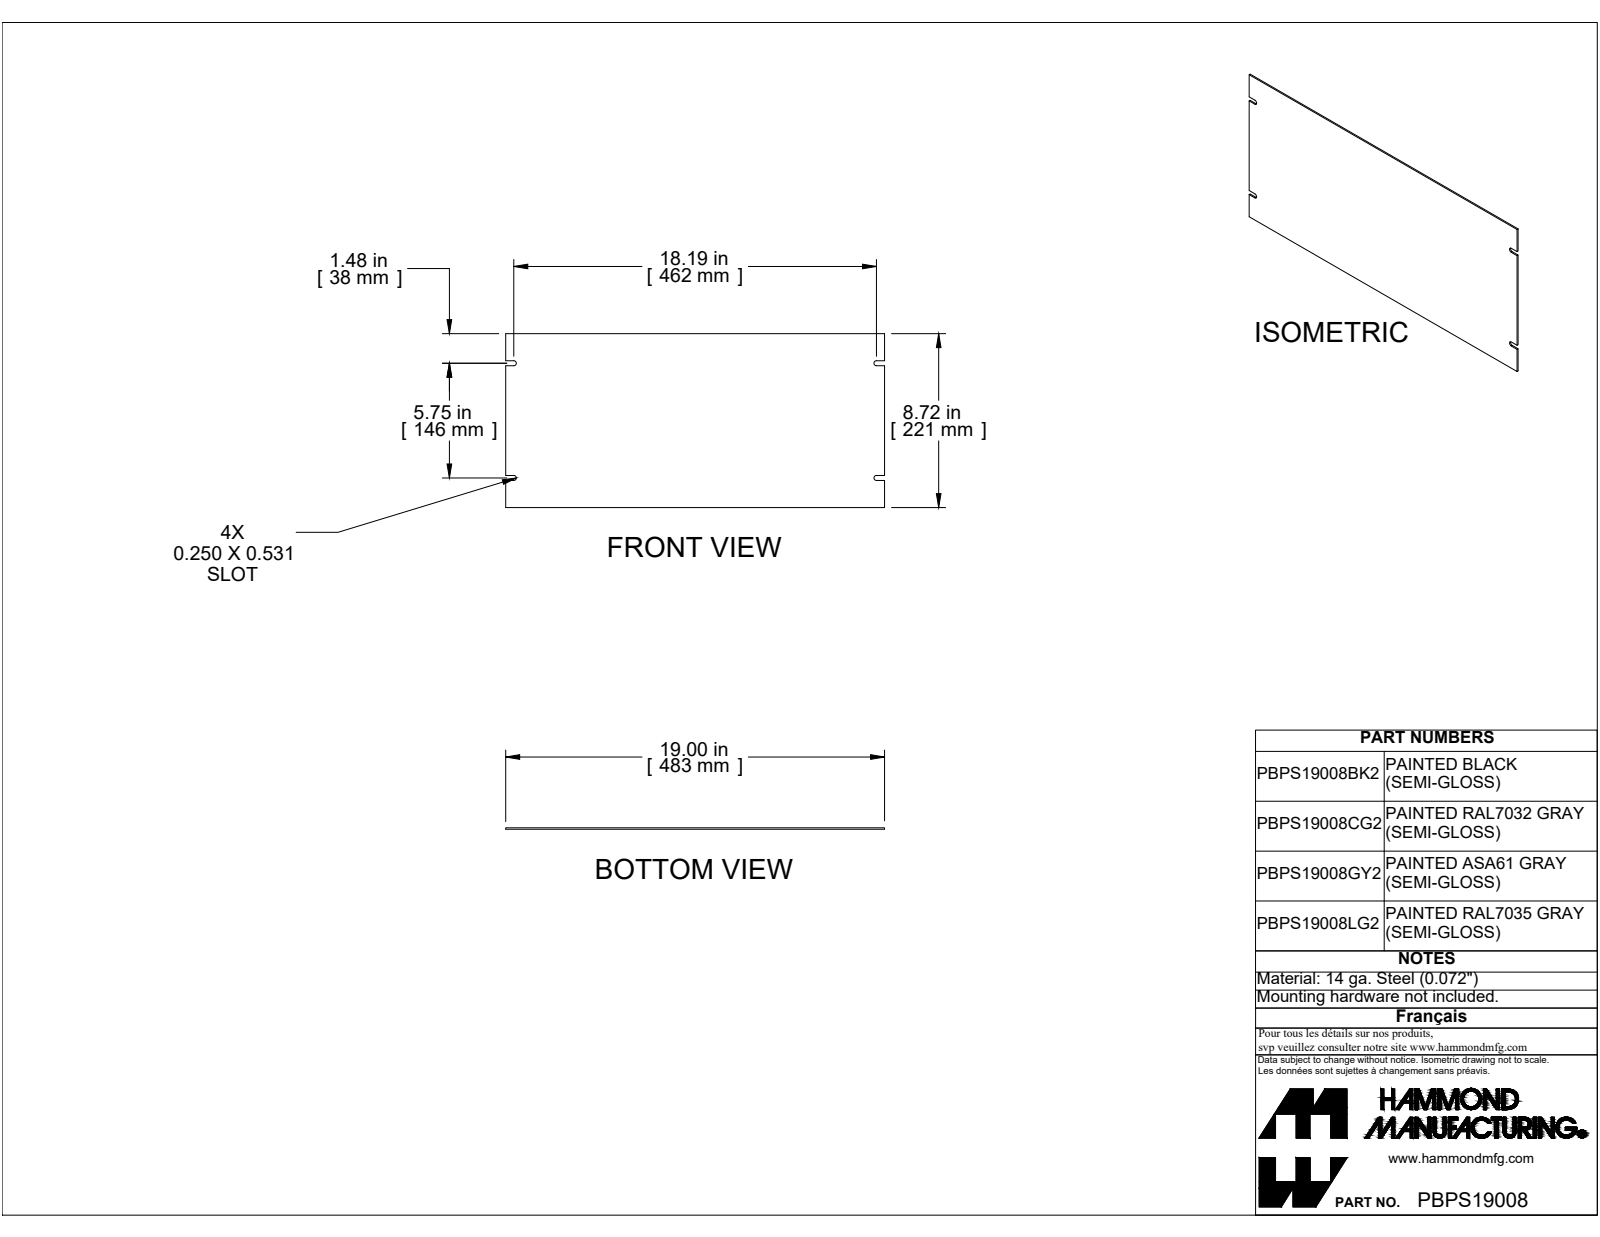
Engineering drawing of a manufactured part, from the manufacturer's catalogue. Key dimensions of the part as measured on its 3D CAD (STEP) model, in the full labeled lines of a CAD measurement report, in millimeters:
Part name (STEP PRODUCT): PBPS19008BK2
STEP written by: SolidWorks 2019 (CONFIG_CONTROL_DESIGN)
Units: millimetres
Bodies: 1 solid, 22 faces (18 planar, 4 cylindrical, 0 other)
Overall size (bounding box): 482.6 × 221.4 × 1.8
Volume: 194 800 mm³ · Surface area: 215 800 mm²
Partial cylindrical surfaces — rounded edges, fillets, slot ends (radius × count): R3.2 ×4
Main face-to-face distances: 1.8, 221.4, 482.6, 34.5, 40.9, 180.6, 186.9, 6.4, 146.1, 152.4
